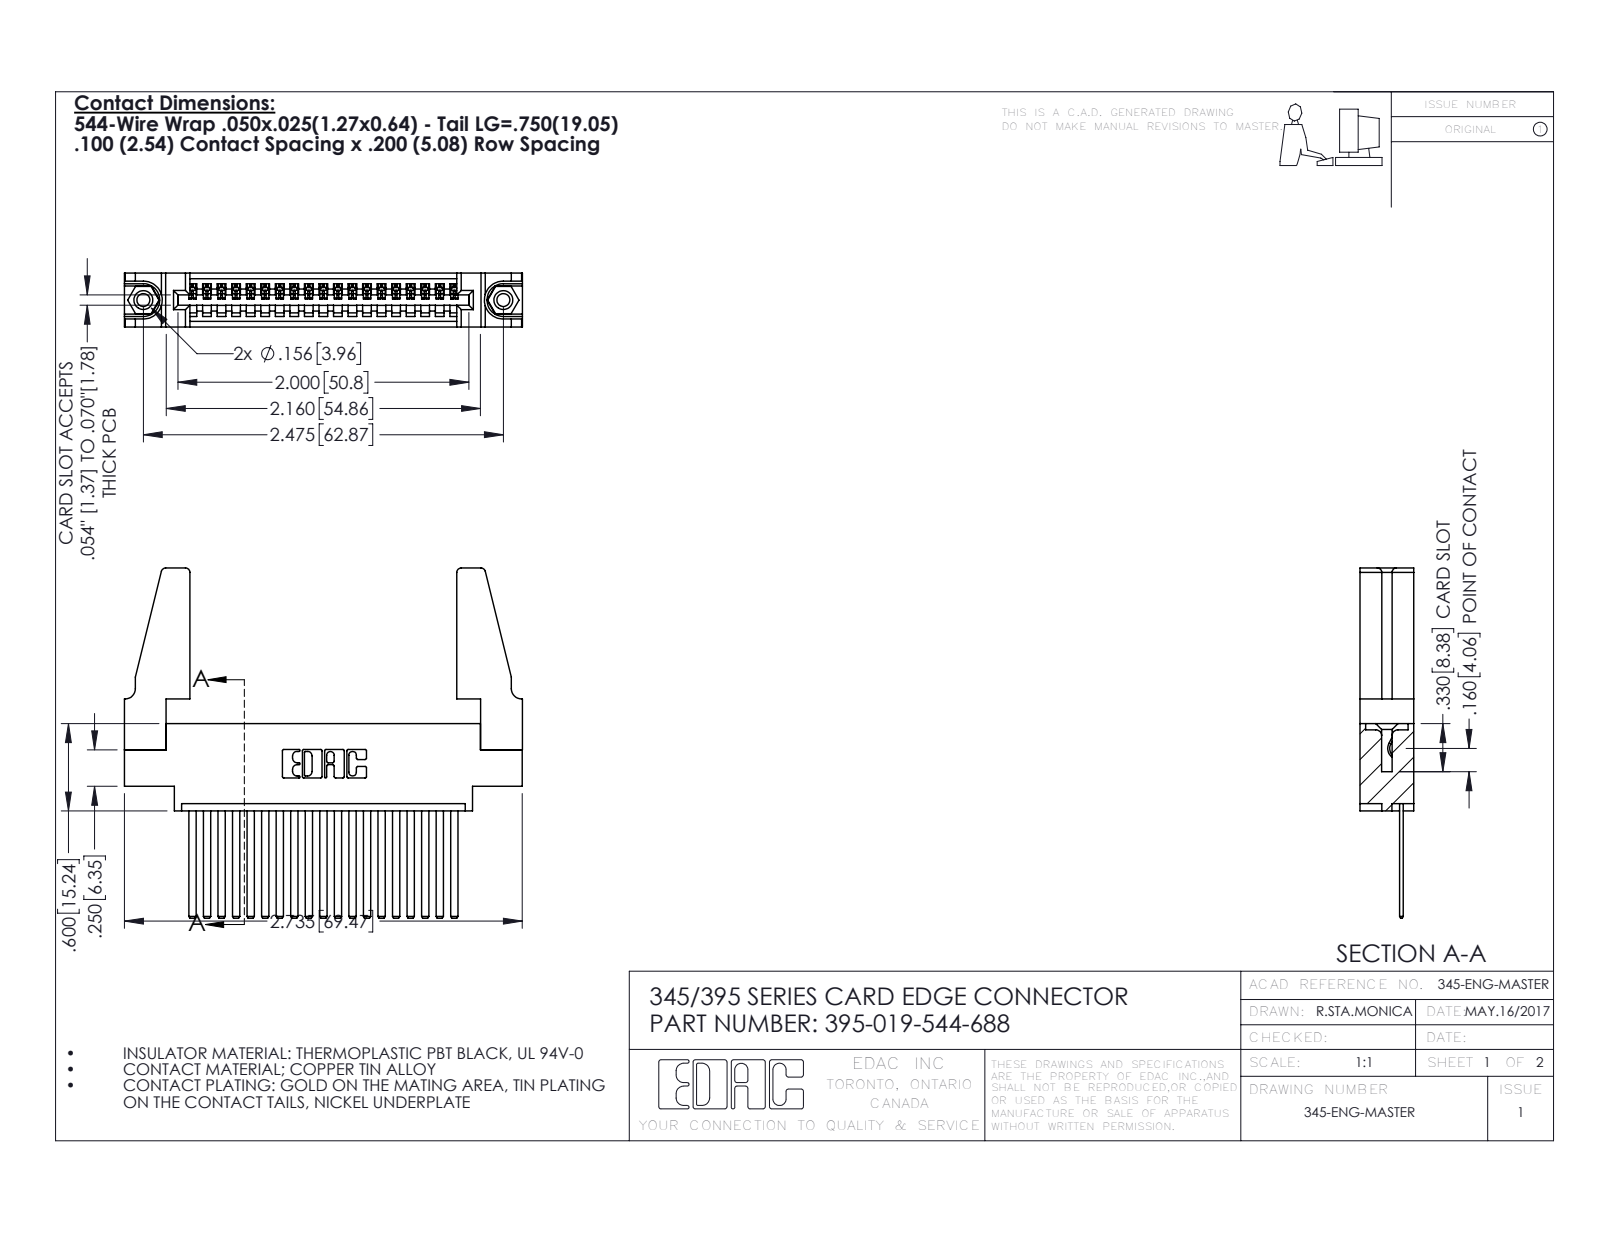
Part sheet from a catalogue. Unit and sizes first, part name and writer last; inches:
Units: inches
Overall size (bounding box): 2.736 × 2.407 × 0.37
Round holes (diameter × count): ⌀0.089 ×2, ⌀0.125 ×2, ⌀0.156 ×2, ⌀0.064 ×1
Round bosses / shafts (diameter × count): ⌀0.155 ×2
Partial cylindrical surfaces — rounded edges, fillets, slot ends (radius × count): R0.006 ×38, R0.01 ×22, R0.03 ×8, R0.007 ×6, R0.031 ×6, R0.026 ×3, R0.031 ×2, R0.04 ×2
Main face-to-face distances: 0.072, 0.37, 0.298, 0.098, 0.272, 0.025, 0.2, 0.225, 0.148, 0.15
Hole centre spacings: 0.27, 2.241, 2.475
Volume: 0.596 in³ · Surface area: 19.01 in²
Bodies: 24 solids, 1242 faces (840 planar, 386 cylindrical, 16 other)
Part name (STEP PRODUCT): 345-250-001_345-250-001-102; 345-292-001_345-293-144; 395-019-544-688; 345-220-078_345-220-088 (+1 more)
STEP written by: SolidWorks 2016 (CONFIG_CONTROL_DESIGN)
